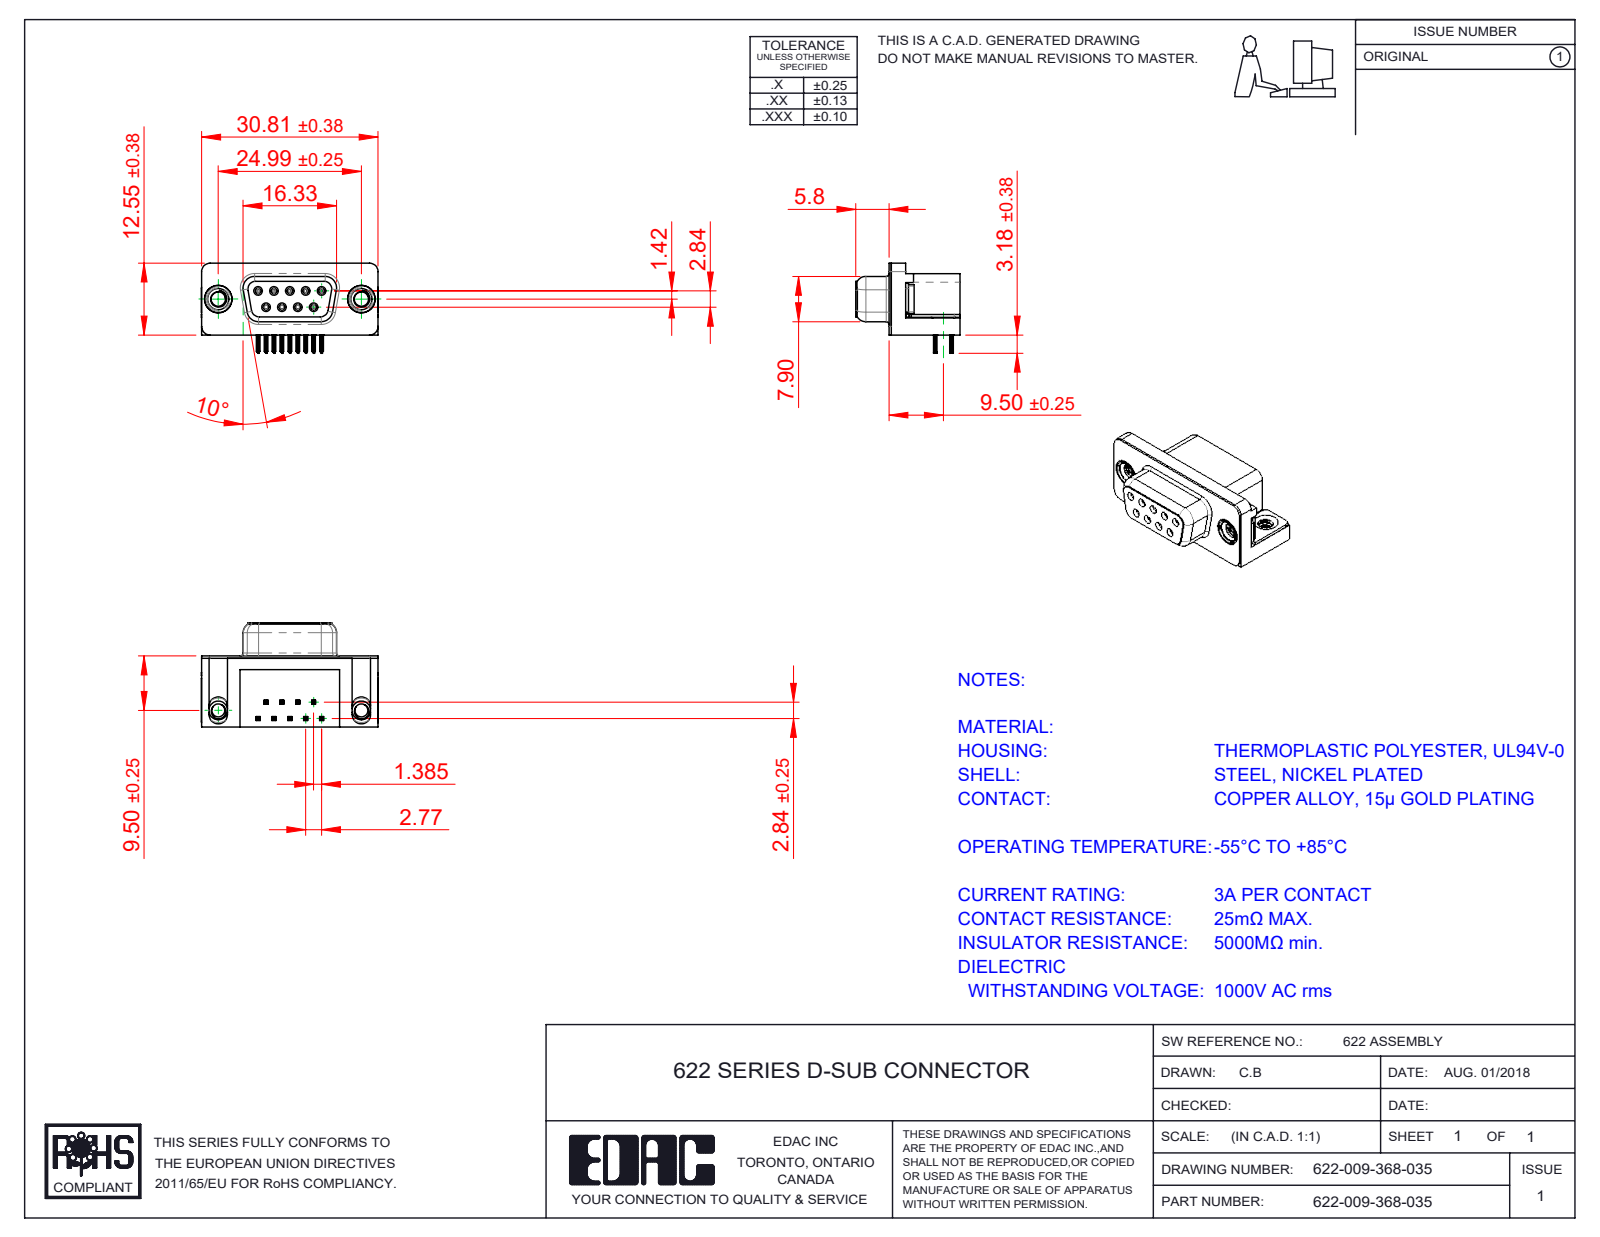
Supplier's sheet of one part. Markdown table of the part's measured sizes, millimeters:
| quantity | value |
| --- | --- |
| part name | 622 Housing_9 Socket; 622 Shell_9 Socket; 622 2 Prong Board Lock; 622 Contact Top (+3 more) |
| STEP written by | SolidWorks 2016 (CONFIG_CONTROL_DESIGN) |
| units | millimeters |
| bodies | 15 solids, 1612 faces (716 planar, 428 cylindrical, 468 other) |
| overall size | 30.89 × 18.2 × 16.25 |
| volume | 3 720 mm³ |
| surface area | 5 082 mm² |
| round holes (diameter × count) | 0.8 × 9, 0.9 × 9, 2.5 × 2, 4 × 2, 4.8 × 2, 5 × 2 |
| round bosses / shafts (diameter × count) | 1.2 × 9, 4.9 × 2, 4.75 × 2, 3.9 × 2 |
| partial cylindrical surfaces (radius × count) | 0.1 × 72, 0.15 × 36, 0.35 × 18, 1 × 18, 0.5 × 10, 0.34 × 9, 0.25 × 8, 1.35 × 8 |
| main face-to-face distances | 0.4, 12, 12.4, 0.35, 2.9, 2.5, 6.2, 10.34, 0.5, 9.5 |
| hole center spacings | 3.16, 2.77, 5.54, 5.03, 5.04, 8.31, 7.48, 7.49 |
